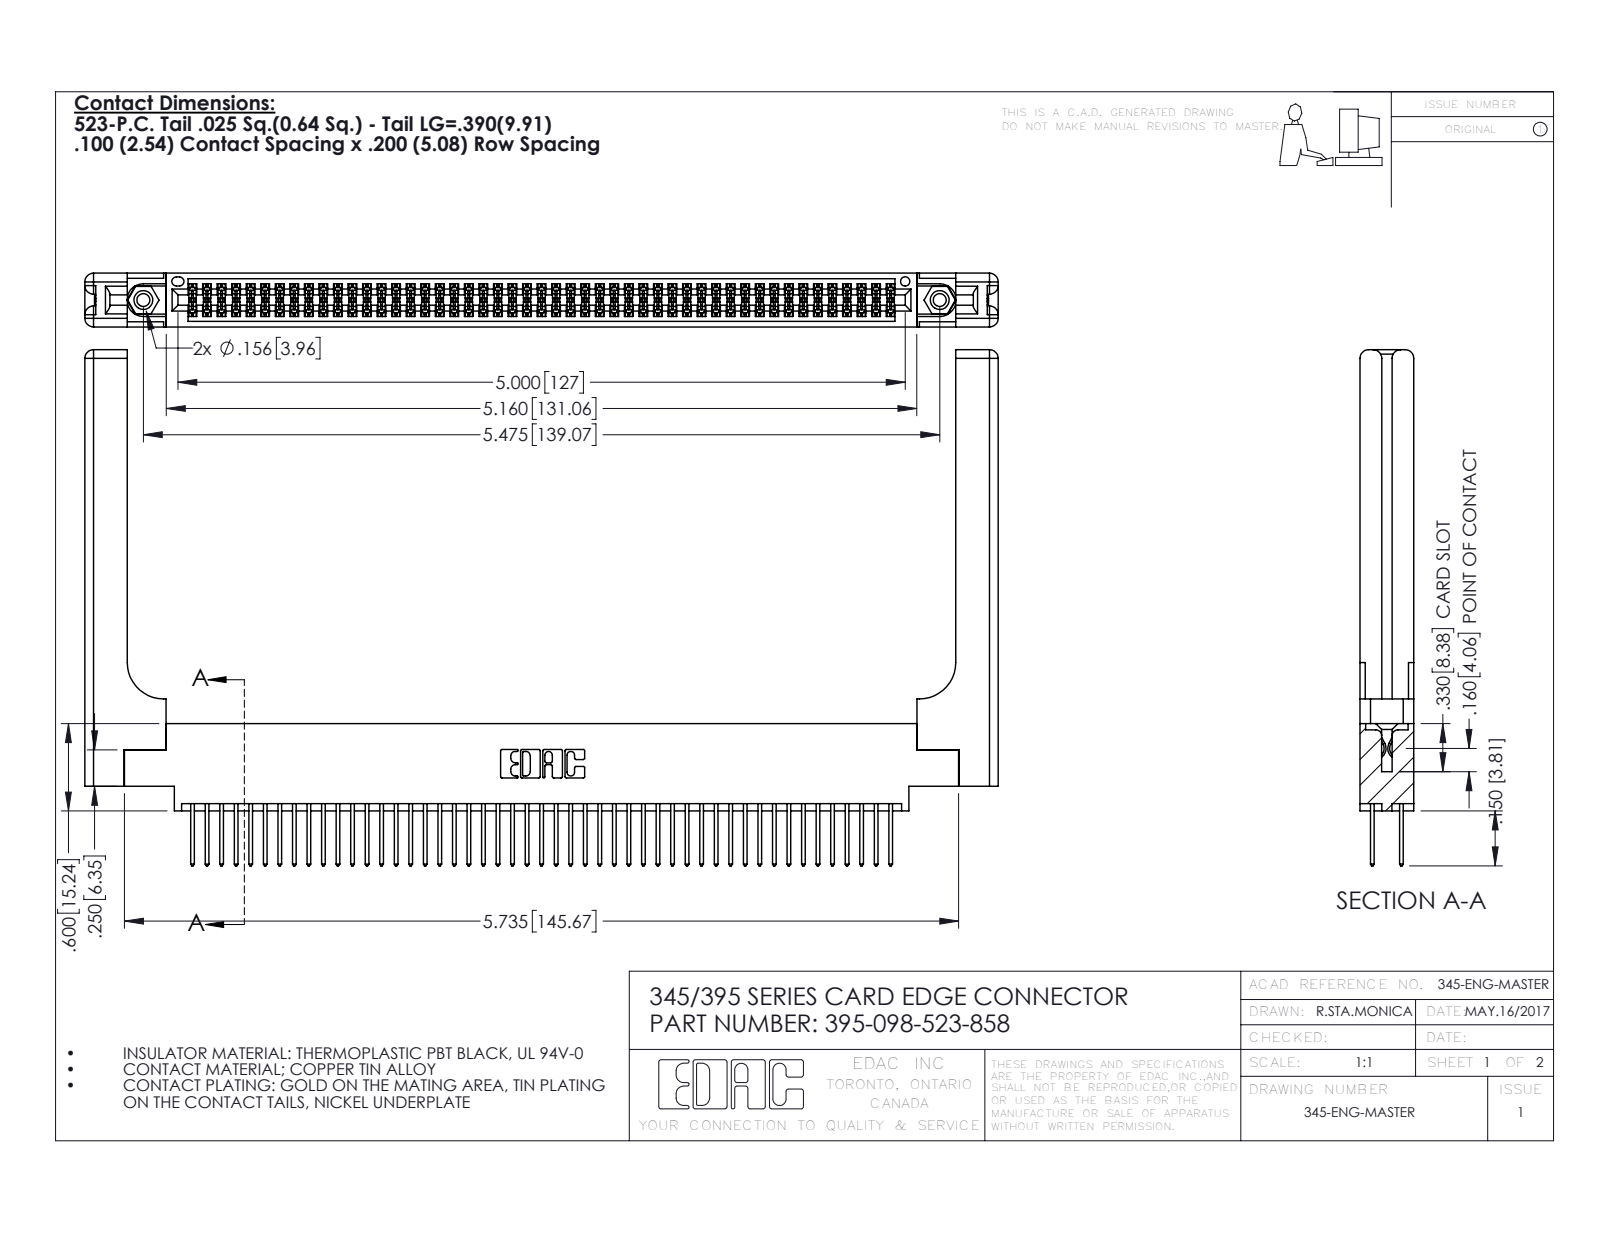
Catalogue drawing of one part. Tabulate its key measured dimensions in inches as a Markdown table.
| quantity | value |
| --- | --- |
| part name | 345-292-001_345-293-123; 345-220-058_345-220-058; 395-098-523-858; 345-250-001_345-250-001-102 (+1 more) |
| STEP written by | SolidWorks 2016 (CONFIG_CONTROL_DESIGN) |
| units | inches |
| bodies | 103 solids, 5286 faces (3466 planar, 1760 cylindrical, 60 other) |
| overall size | 6.279 × 3.547 × 0.37 |
| volume | 1.472 in³ |
| surface area | 45.52 in² |
| round holes (diameter × count) | 0.089 × 2, 0.125 × 2, 0.156 × 2, 0.064 × 1 |
| round bosses / shafts (diameter × count) | 0.155 × 2 |
| partial cylindrical surfaces (radius × count) | 0.006 × 147, 0.01 × 98, 0.01 × 22, 0.06 × 16, 0.007 × 6, 0.031 × 6, 0.026 × 3, 0.014 × 2 |
| main face-to-face distances | 0.072, 0.298, 0.37, 0.098, 0.272, 0.025, 0.2, 0.225, 0.175, 0.148 |
| hole center spacings | 0.27, 5.239, 5.475 |
